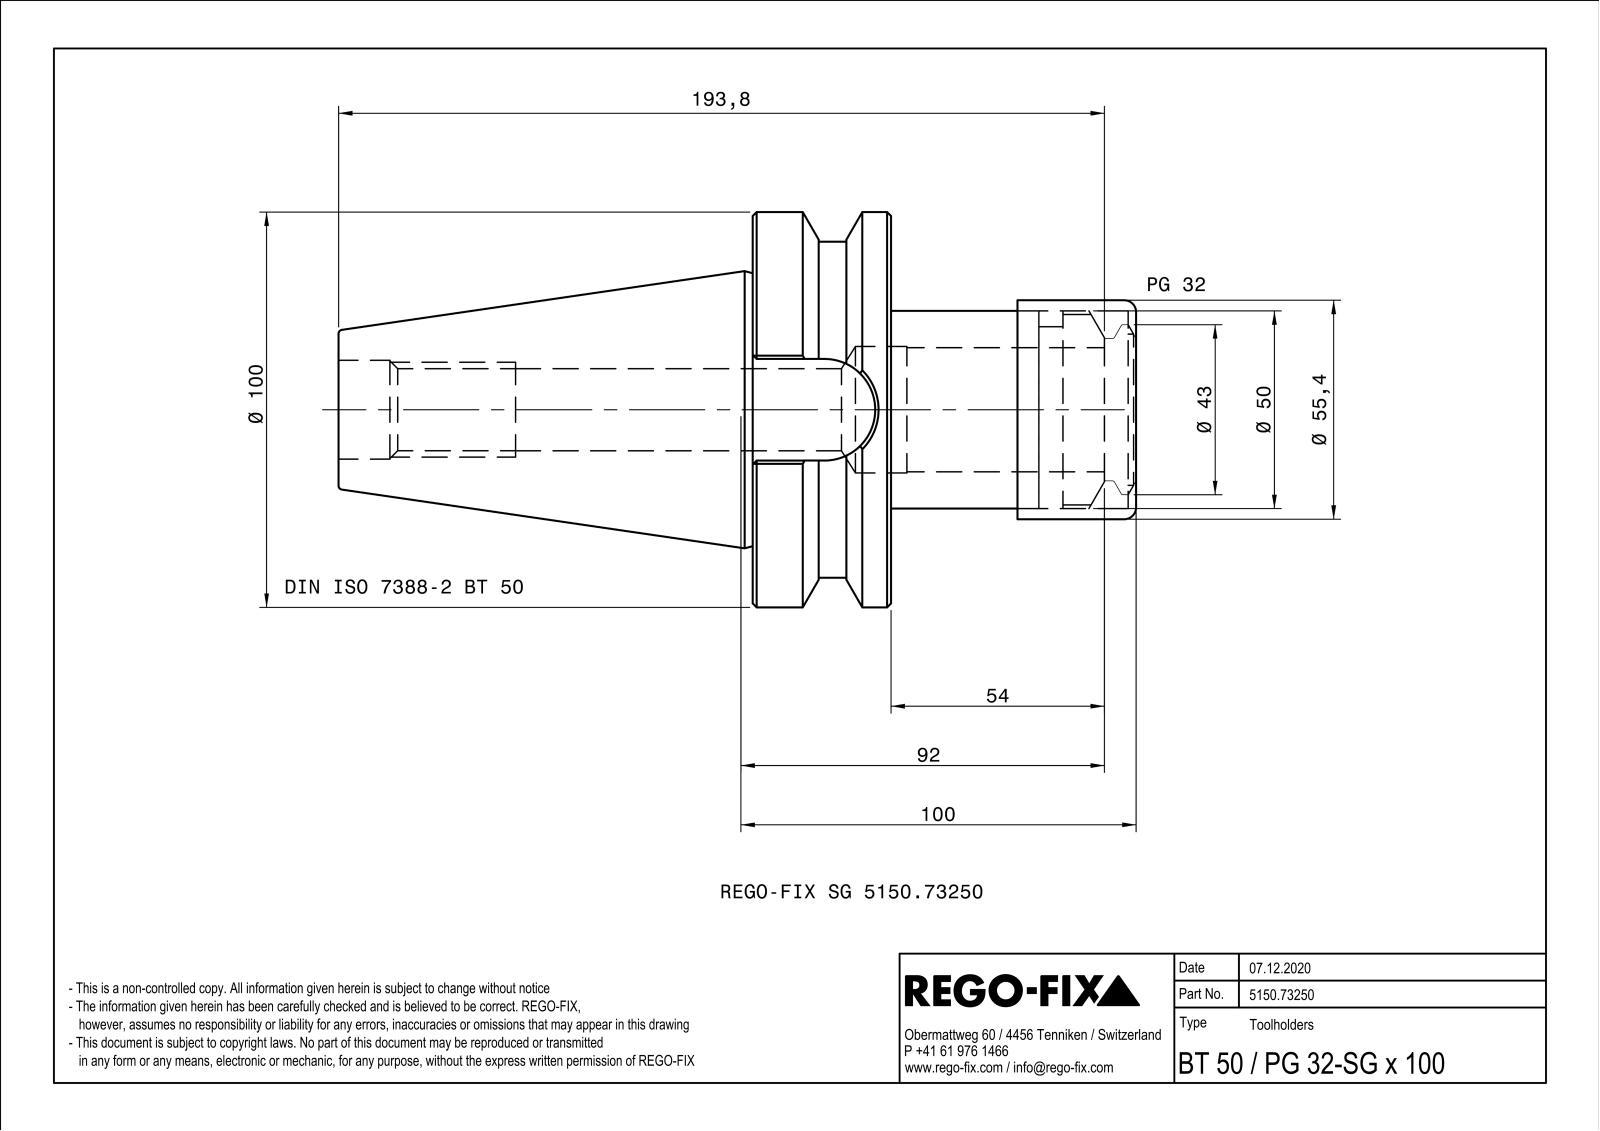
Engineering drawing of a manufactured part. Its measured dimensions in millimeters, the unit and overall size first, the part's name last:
Units: millimetres
Overall size (bounding box): 201.8 × 100 × 100
Round holes (diameter × count): ⌀20.75 ×1, ⌀25 ×1, ⌀33 ×1, ⌀38.25 ×1, ⌀48.38 ×1, ⌀50.05 ×1, ⌀51 ×1
Round bosses / shafts (diameter × count): ⌀100 ×1, ⌀85 ×1, ⌀55.4 ×1, ⌀55 ×1, ⌀50 ×1, ⌀42 ×1
Partial cylindrical surfaces — rounded edges, fillets, slot ends (radius × count): R0.5 ×4, R12.85 ×1
Main face-to-face distances: 35, 62, 97, 70.7, 201.8, 139.8, 104.8, 24.6, 37.4, 72.4
Volume: 510 802 mm³ · Surface area: 79 503 mm²
Bodies: 2 solids, 97 faces (34 planar, 24 cylindrical, 39 other)
Part name (STEP PRODUCT): 0013427
STEP written by: SIEMENS PLM Software Solid Edge ST10 (AUTOMOTIVE_DESIGN)
